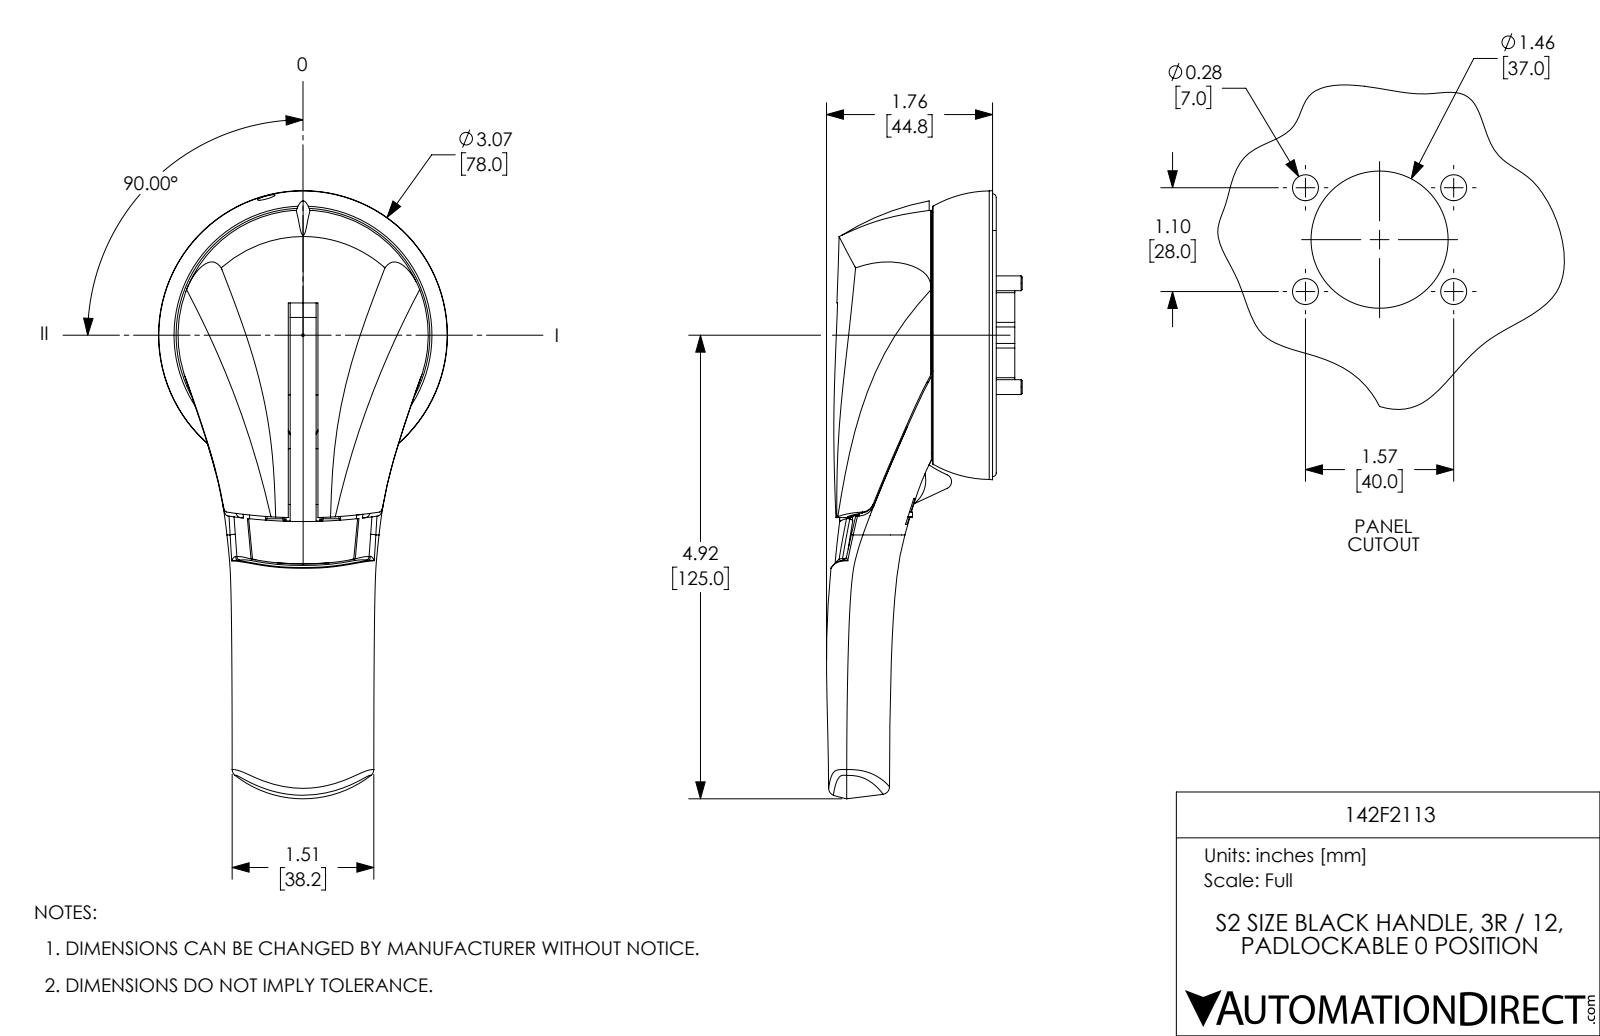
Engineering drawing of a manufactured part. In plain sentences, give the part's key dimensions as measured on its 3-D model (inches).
The part is named "142F2113". Its 3-D file was written by "SolidWorks 2017 (AUTOMOTIVE_DESIGN)". It is 8 solids with 1516 faces: 810 planar, 548 cylindrical and 158 other. Overall it measures 6.458 by 3.07 by 2.079 inches. Its volume is 9.514 cubic inches and its surface area 87.31 square inches. Round holes: 6 of diameter 0.157, 4 of diameter 0.339, 4 of diameter 0.425, 3 of diameter 0.03, 2 of diameter 0.169, 2 of diameter 0.362, 1 of diameter 0.118, 1 of diameter 0.189, 1 of diameter 2.992. Round bosses or shafts: 11 of diameter 0.02, 4 of diameter 0.335, 4 of diameter 0.315, 3 of diameter 0.089, 3 of diameter 0.069, 2 of diameter 0.228, 1 of diameter 2.819, 1 of diameter 2.701. Partial cylindrical surfaces (rounded edges, fillets, slot ends): 221 of radius 0.01, 20 of radius 0.015, 20 of radius 0.034, 15 of radius 0.03, 4 of radius 0.039, 3 of radius 0.025, 3 of radius 5.437, 2 of radius 0.079. The main face-to-face distances are 0.024, 0.701, 0.713, 0.689, 0.035, 0.102, 0.276, 0.173, 0.244, 0.047. The hole center spacings are 0.961, 0.309, 0.669, 1.098, 1.102, 1.203, 1.575, 1.881.
